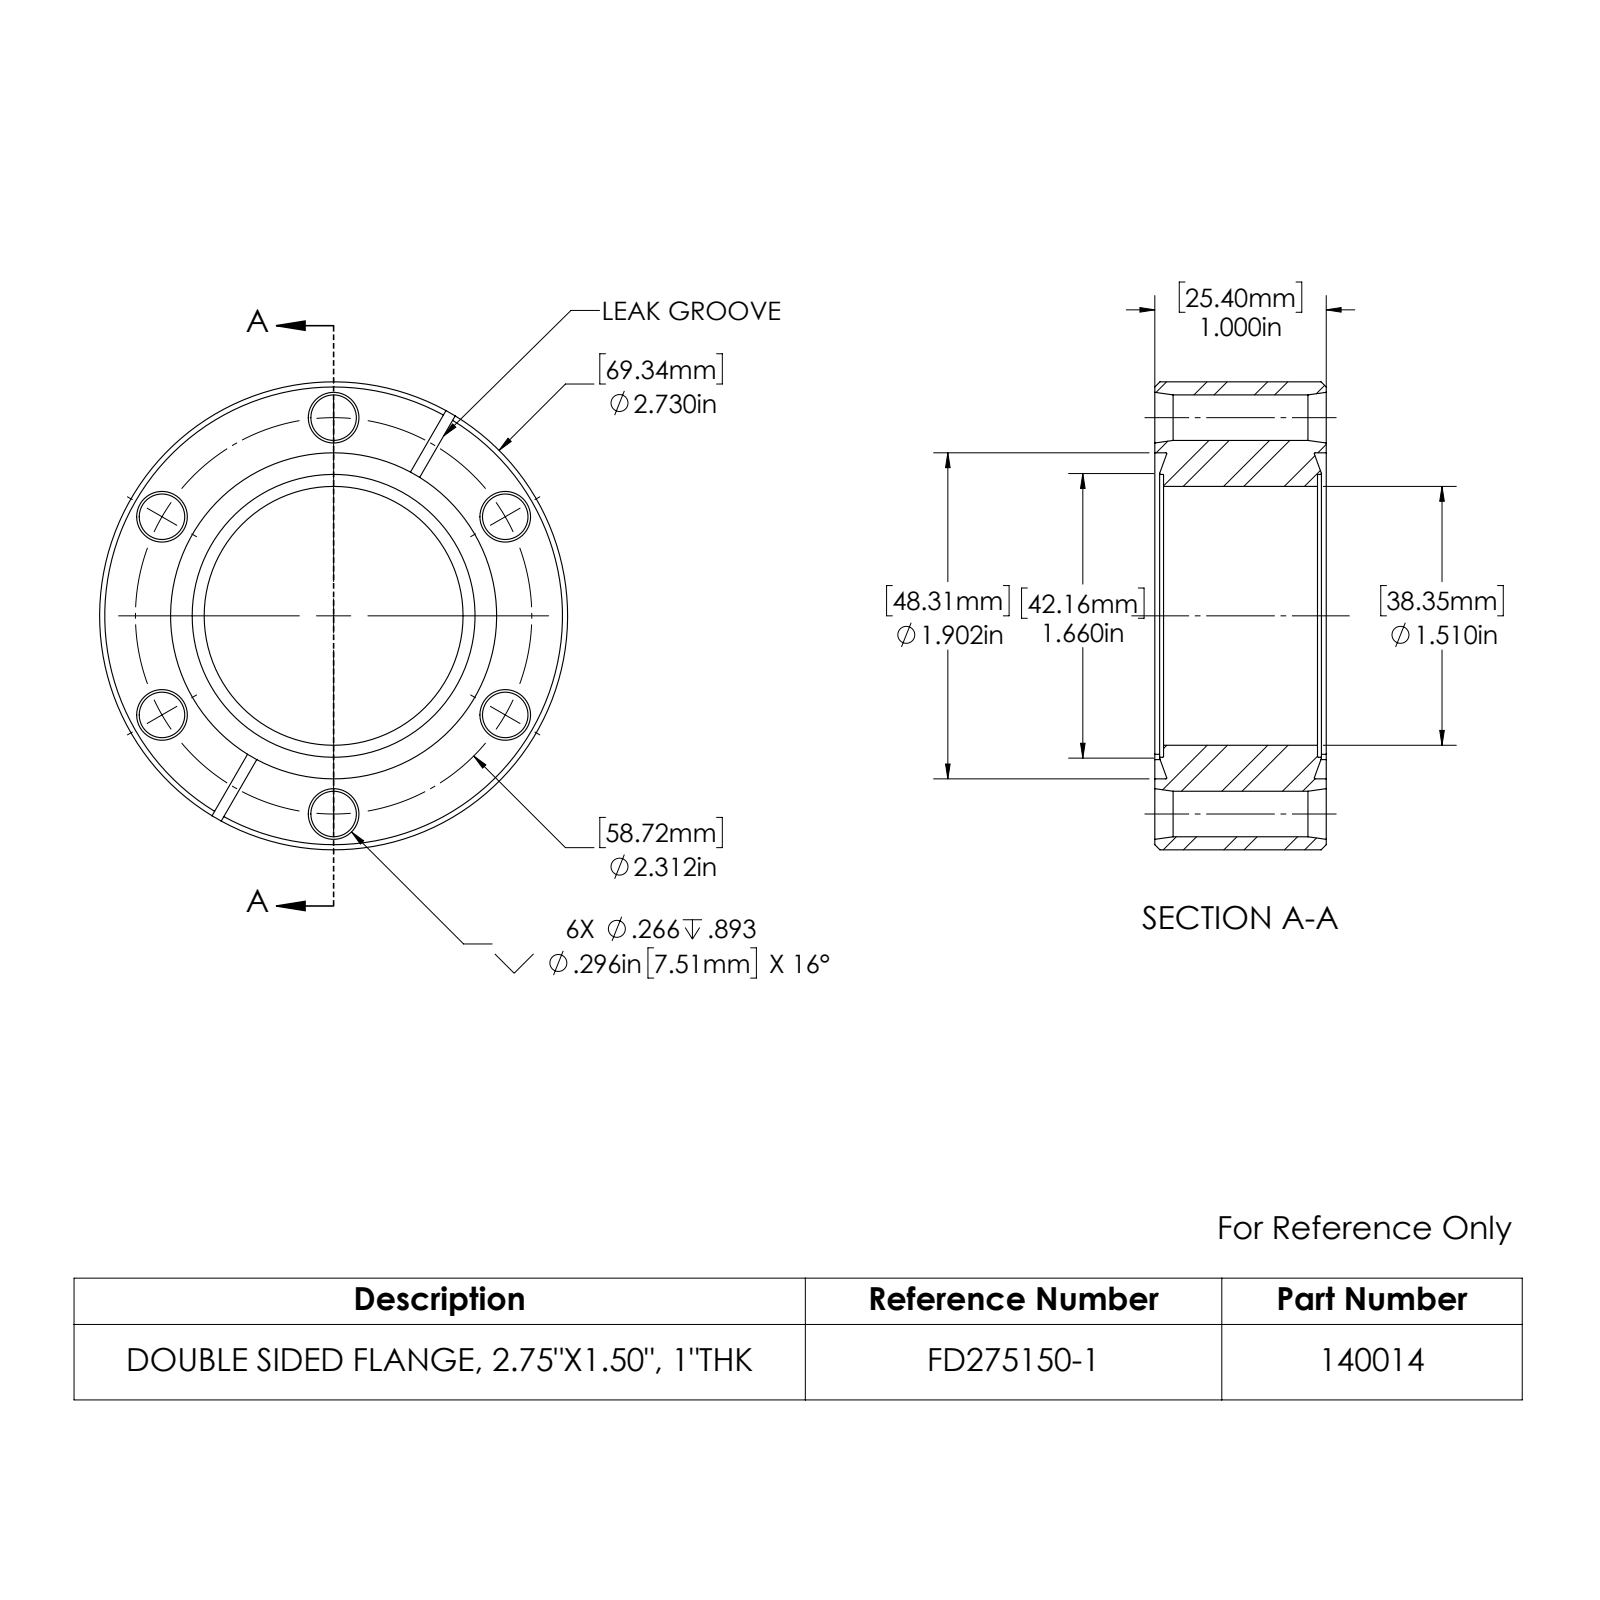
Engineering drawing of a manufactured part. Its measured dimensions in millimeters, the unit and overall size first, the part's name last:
Units: millimetres
Overall size (bounding box): 69.3 × 69.3 × 25.4
Round holes (diameter × count): ⌀6.8 ×6, ⌀38.4 ×1, ⌀41.9 ×1, ⌀48.3 ×1
Round bosses / shafts (diameter × count): ⌀69.3 ×1
Partial cylindrical surfaces — rounded edges, fillets, slot ends (radius × count): R31.8 ×4
Main face-to-face distances: 25.4, 1.3, 24.1, 22.8, 1.6
Hole centre spacings: 29.4, 50.9, 50.9, 58.7, 58.7
Volume: 58 960 mm³ · Surface area: 16 970 mm²
Bodies: 1 solid, 88 faces (14 planar, 28 cylindrical, 46 other)
Part name (STEP PRODUCT): 140014_A
STEP written by: SolidWorks 2022 (CONFIG_CONTROL_DESIGN)
